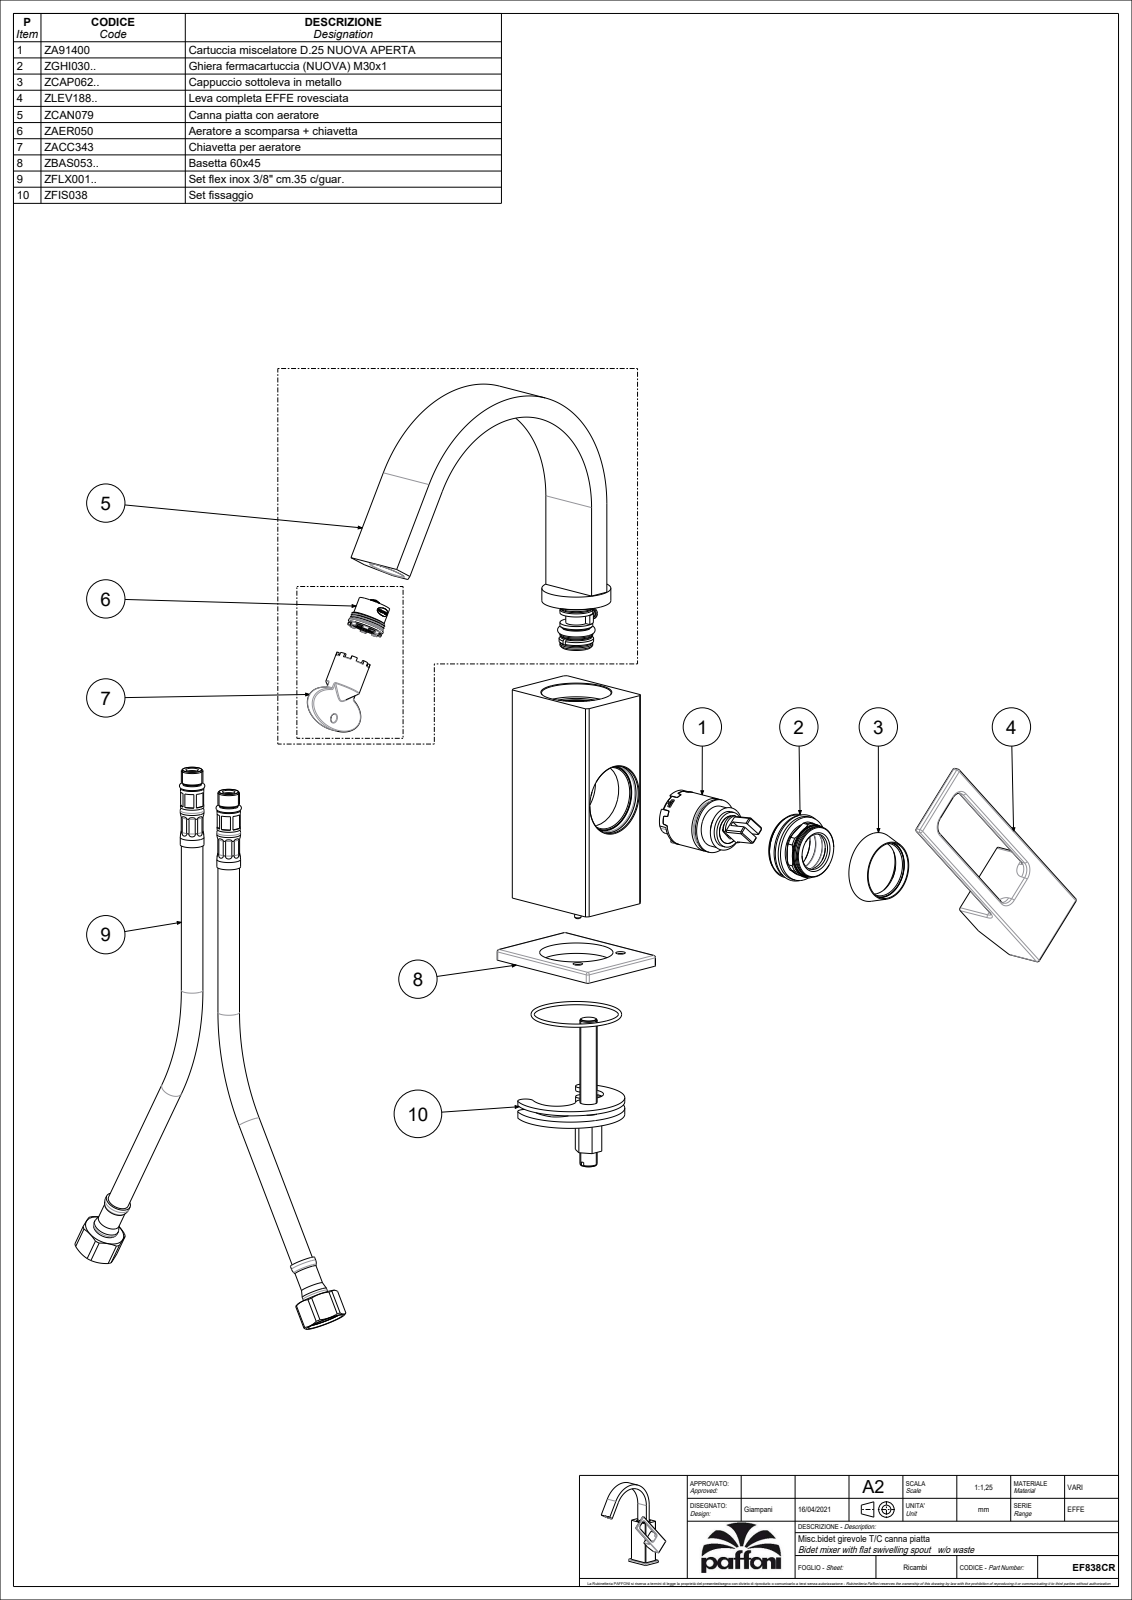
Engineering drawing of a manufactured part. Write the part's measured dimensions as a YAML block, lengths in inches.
part_name: "EF838CR"
step_written_by: "CREO PARAMETRIC BY PTC INC, 2020044 (CONFIG_CONTROL_DESIGN)"
units: inches
bodies: {solids: 3, faces: 3149, planar: 1988, cylindrical: 685, other: 476}
overall_size: [8.268, 6.223, 3.279]
volume: 13.46
surface_area: 147.9
round_holes:
  - {diameter: 0.177, count: 3}
  - {diameter: 0.236, count: 3}
  - {diameter: 0.118, count: 2}
  - {diameter: 0.13, count: 2}
  - {diameter: 0.197, count: 2}
  - {diameter: 0.217, count: 2}
  - {diameter: 0.256, count: 2}
  - {diameter: 0.276, count: 2}
  - {diameter: 0.157, count: 1}
  - {diameter: 0.268, count: 1}
  - {diameter: 0.307, count: 1}
  - {diameter: 0.315, count: 1}
round_bosses_or_shafts:
  - {diameter: 0.035, count: 3}
  - {diameter: 0.413, count: 2}
  - {diameter: 0.299, count: 2}
  - {diameter: 1.528, count: 1}
  - {diameter: 1.26, count: 1}
  - {diameter: 0.984, count: 1}
  - {diameter: 0.89, count: 1}
  - {diameter: 0.787, count: 1}
partial_cylinders:
  - {radius: 0.02, count: 64}
  - {radius: 0.005, count: 51}
  - {radius: 0.039, count: 39}
  - {radius: 0.028, count: 10}
  - {radius: 0.024, count: 8}
  - {radius: 0.059, count: 8}
  - {radius: 0.031, count: 6}
  - {radius: 0.197, count: 5}
face_to_face_distances: [0.394, 0.059, 1.417, 1.575, 0.453, 1.516, 1.122, 1.181, 0.906, 0.335]
hole_center_spacings: [0.265, 0.371, 0.398, 0.441, 0.445, 0.601, 0.711, 0.118]
